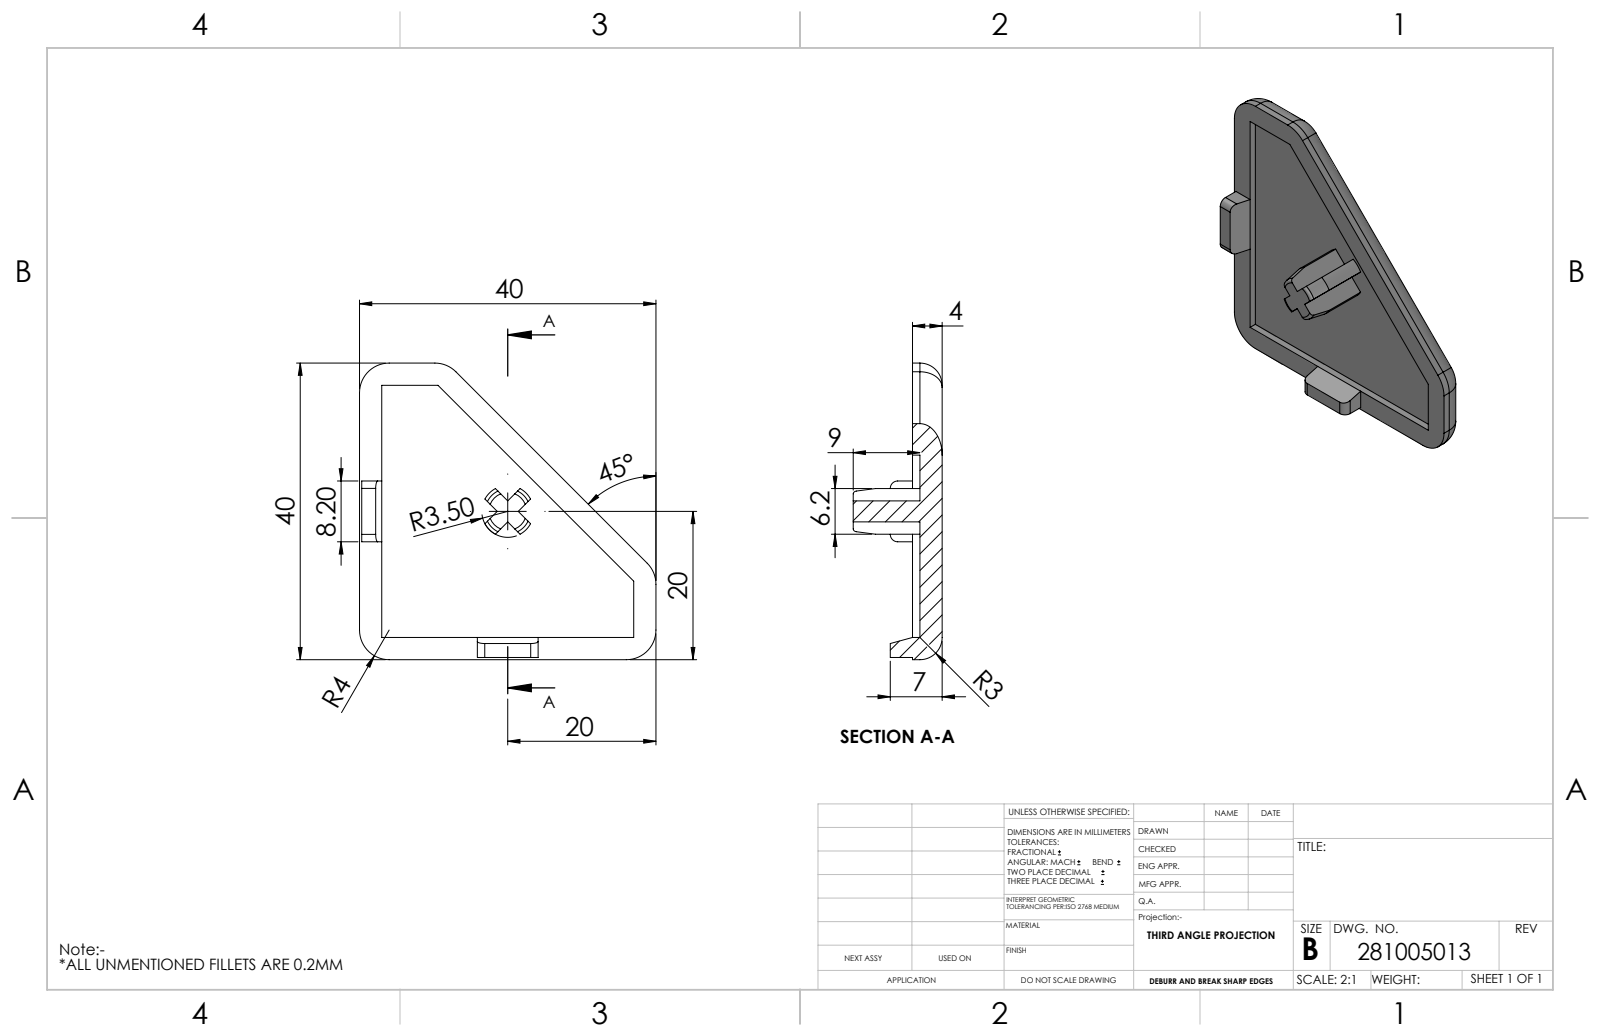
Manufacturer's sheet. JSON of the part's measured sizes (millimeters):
{"part_name": "281005013 Abdeckkappe 40x40 - 45", "step_written_by": "Autodesk Inventor 2019 (AUTOMOTIVE_DESIGN)", "units": "millimeters", "bodies": {"solids": 1, "faces": 63, "planar": 32, "cylindrical": 18, "other": 13}, "overall_size": [40, 40, 12], "volume_mm3": 4020, "surface_area_mm2": 3215, "partial_cylinders_radius": [[3, 5], [4, 5], [1, 4], [3.5, 1]], "face_to_face_distances": [3, 4, 1, 2, 2.7, 4.36, 6.36, 7.36, 9.36, 37]}
